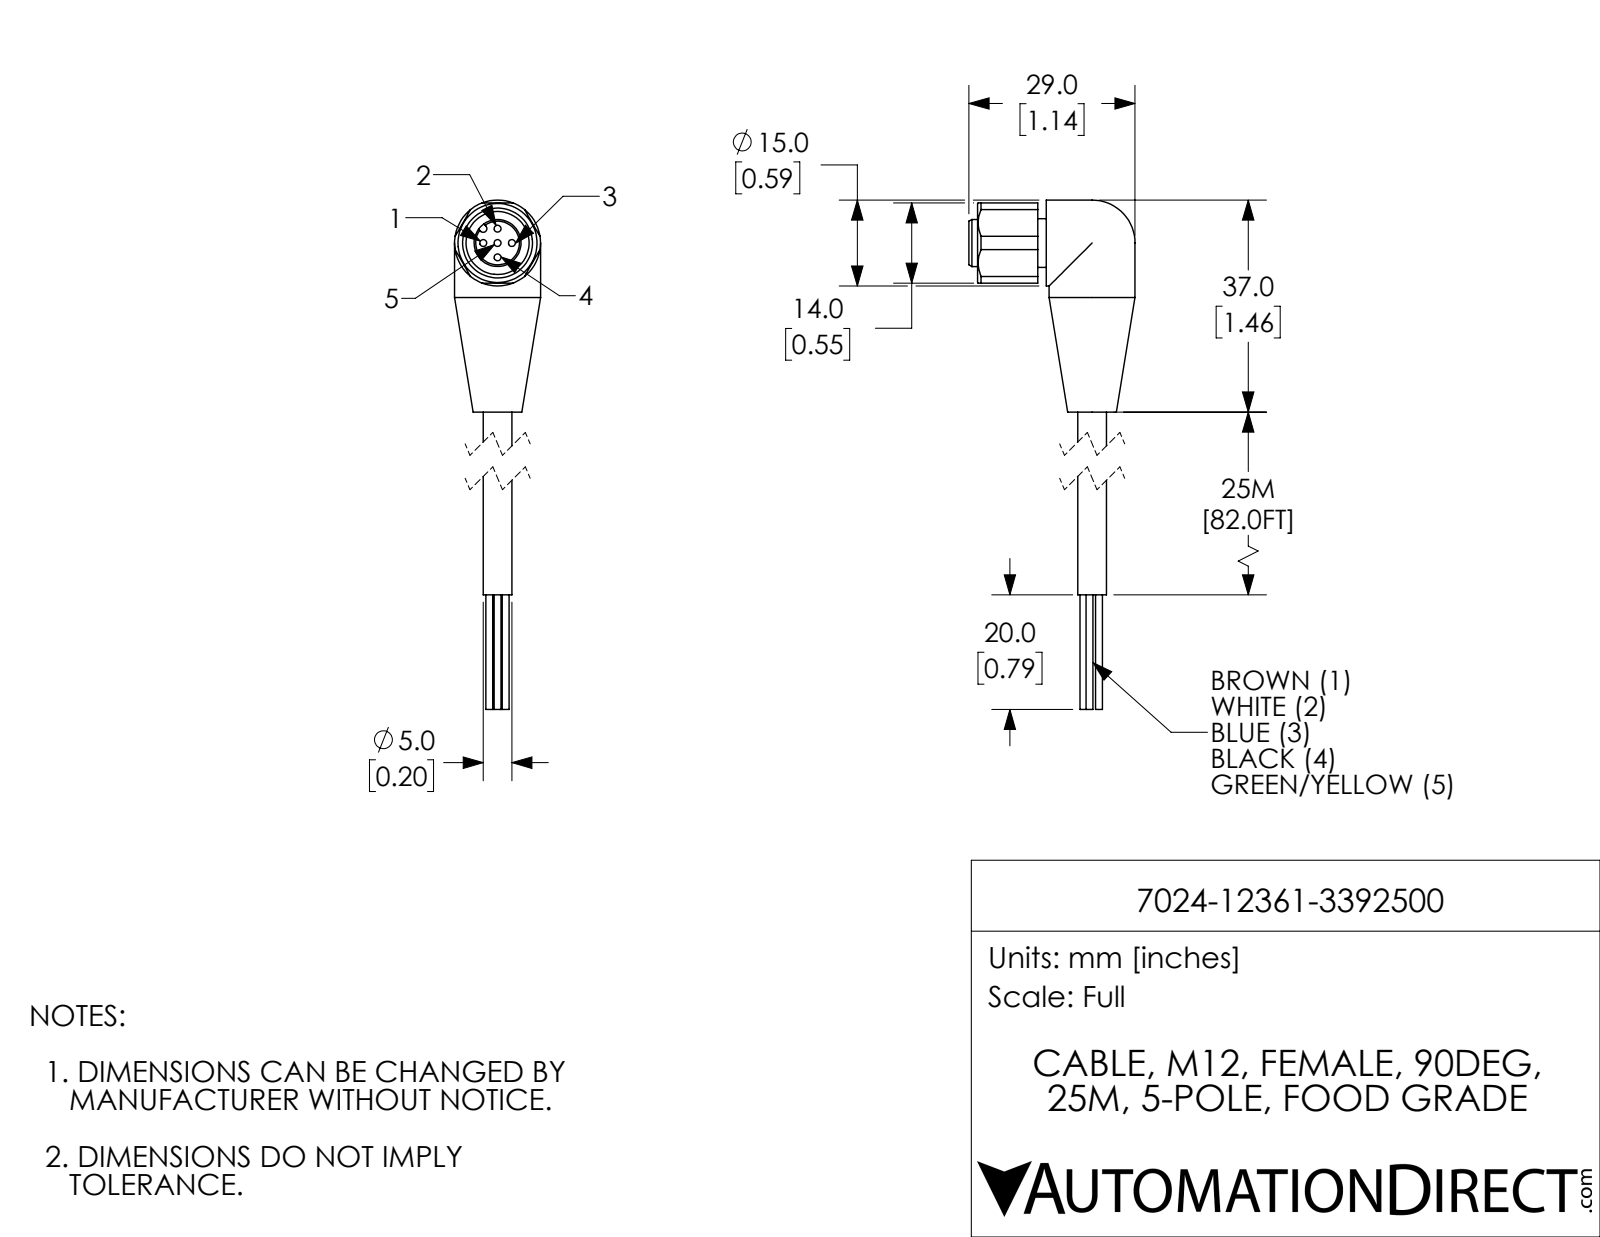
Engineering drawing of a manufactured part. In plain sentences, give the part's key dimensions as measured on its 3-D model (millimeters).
The part is named "7024-12361-3392500". Its 3-D file was written by "SolidWorks 2018 (AUTOMOTIVE_DESIGN)". It is 1 solid with 76 faces: 26 planar, 40 cylindrical and 10 other. Overall it measures 87 by 29 by 15 millimeters. Its volume is 7 424 cubic millimeters and its surface area 3 961 square millimeters. Round holes: 5 of diameter 1.2, 1 of diameter 11. Round bosses or shafts: 5 of diameter 1.2, 2 of diameter 15, 1 of diameter 8.5, 1 of diameter 8.2, 1 of diameter 5. Partial cylindrical surfaces (rounded edges, fillets, slot ends): 1 of radius 0.65. The main face-to-face distances are 14, 1.5, 12, 4.5, 3, 13.5, 9, 22.5, 36.5, 10.5. The hole center spacings are 2.5, 3.54, 5.
